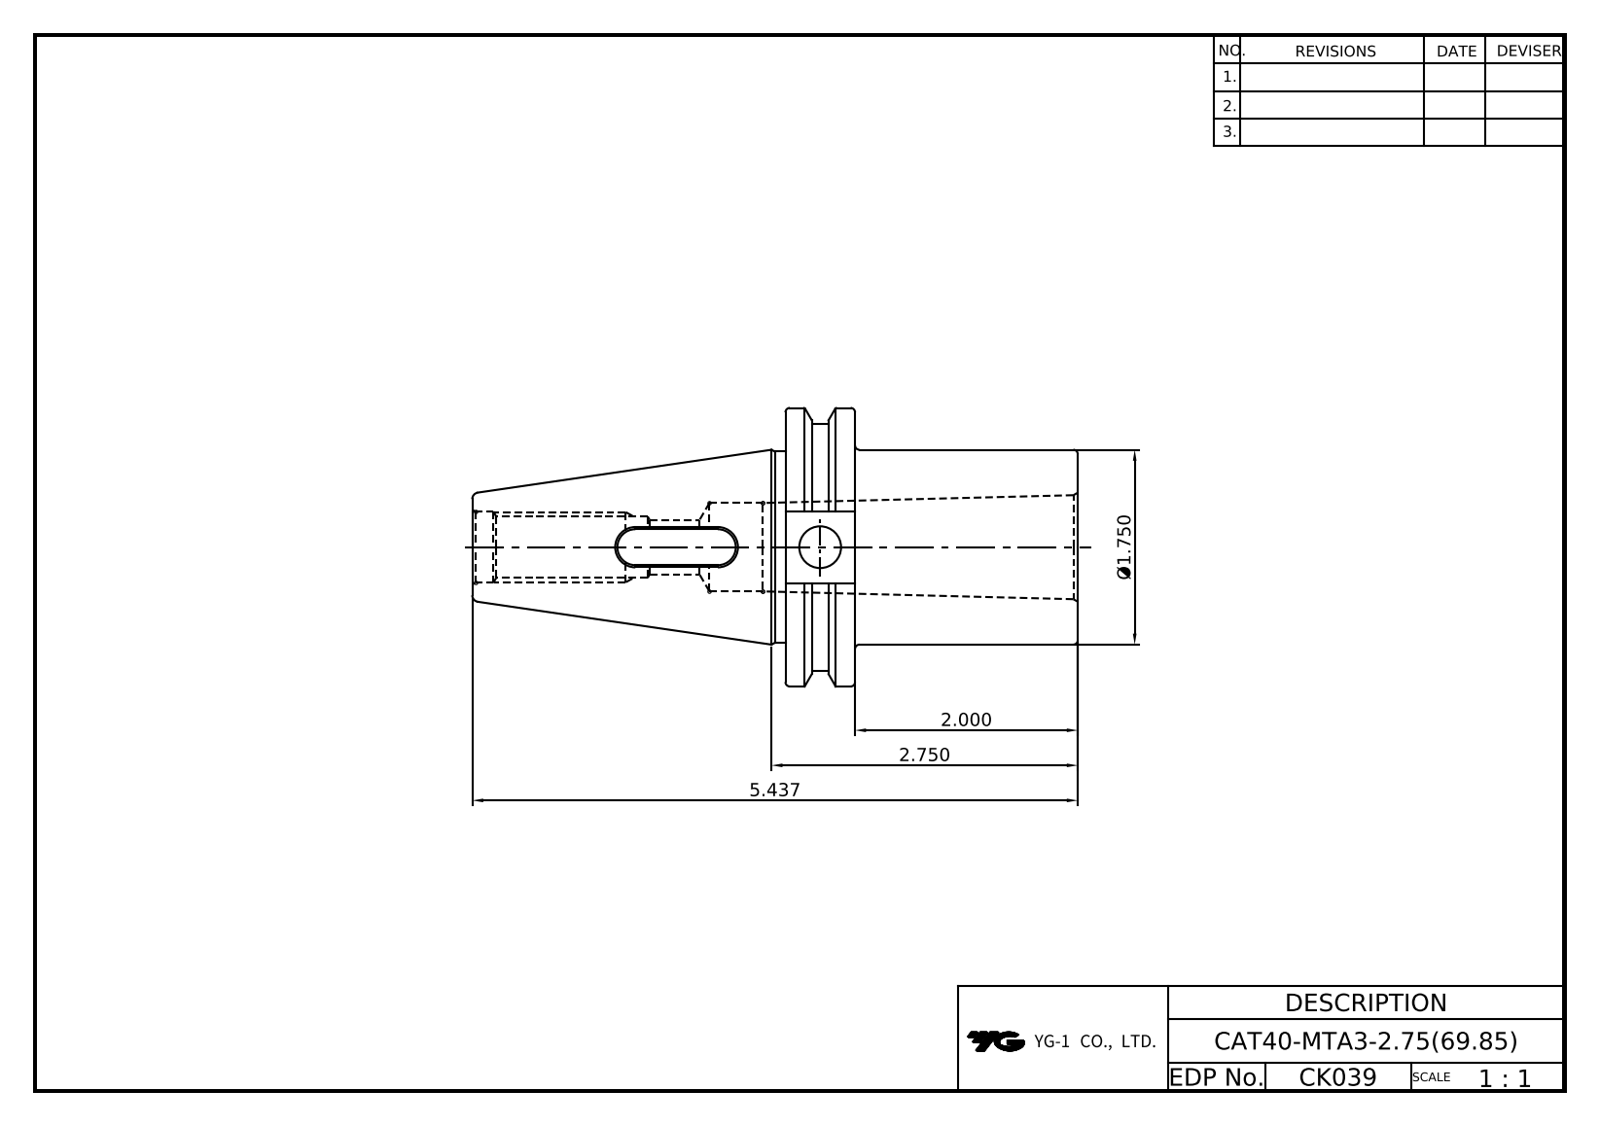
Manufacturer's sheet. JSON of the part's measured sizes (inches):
{"part_name": "LO-CAT40-MTA3-69.85", "step_written_by": "Autodesk Inventor 2025 (AUTOMOTIVE_DESIGN)", "units": "inches", "bodies": {"solids": 1, "faces": 83, "planar": 33, "cylindrical": 16, "other": 34}, "overall_size": [5.437, 2.5, 2.405], "volume_in3": 9.052, "surface_area_in2": 49.32, "round_holes": [[0.375, 1], [0.527, 1], [0.642, 1], [0.795, 1]], "round_bosses_or_shafts": [[2.5, 1], [2.217, 1], [1.75, 1], [1.717, 1]], "partial_cylinders_radius": [[0.156, 2]], "face_to_face_distances": [0.625, 2.625, 2, 0.311, 0.167, 0.478, 1.874, 0.645, 2.812, 3.437]}
